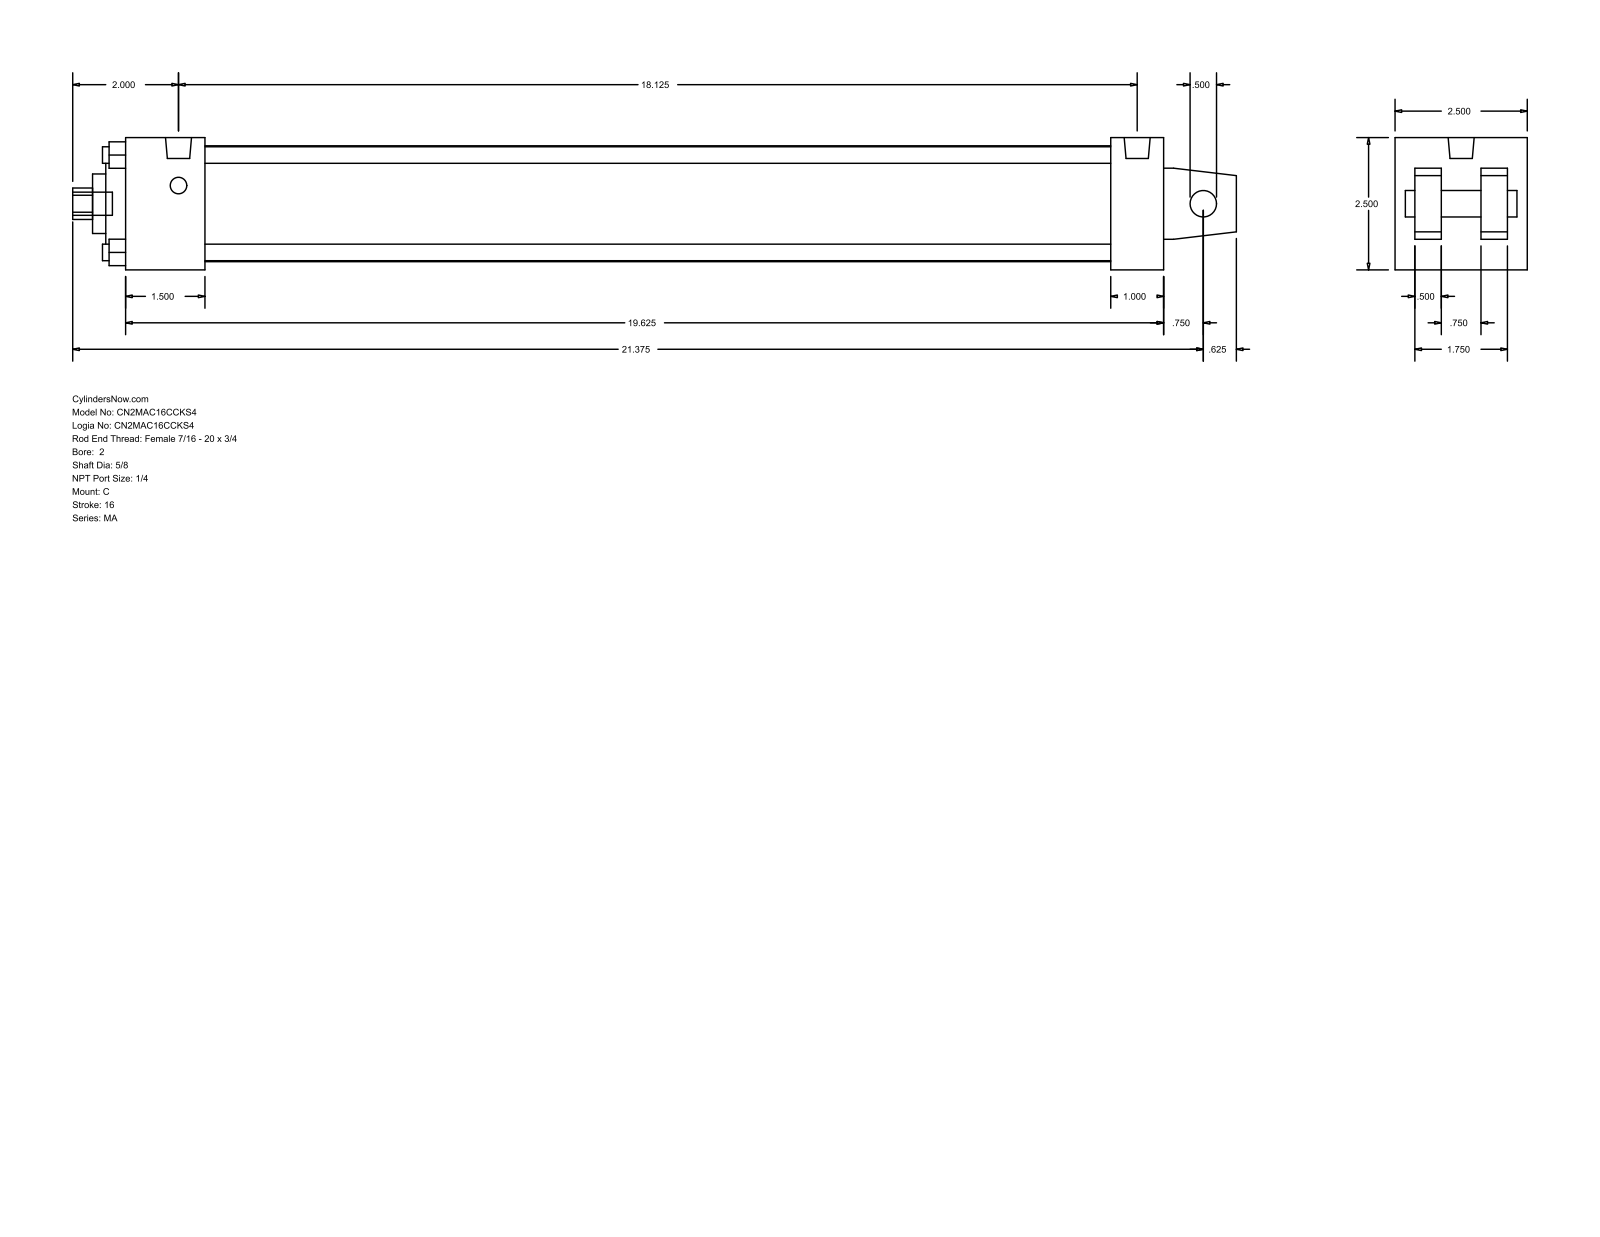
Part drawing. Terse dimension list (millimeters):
name: MA_C__0200_0.625
written by: GSSL Pune (CONFIG_CONTROL_DESIGN)
unit: mm
bodies: 0 solids, 105 faces (77 planar, 28 cylindrical, 0 other)
size: 558.8 × 63.5 × 63.5
holes: 4× ⌀7.94, 1× ⌀12.7, 1× ⌀15.88, 1× ⌀28.57, 1× ⌀50.8, 1× ⌀55.63
bosses: 4× ⌀7.94, 2× ⌀12.49, 1× ⌀11.11
rounds: 1× R7.54
face distances: 63.5, 9.52, 12.7, 22.22, 41.28, 53.98, 31.76, 25.4, 38.1, 498.48
hole spacings: 33.05, 46.74, 66.1
